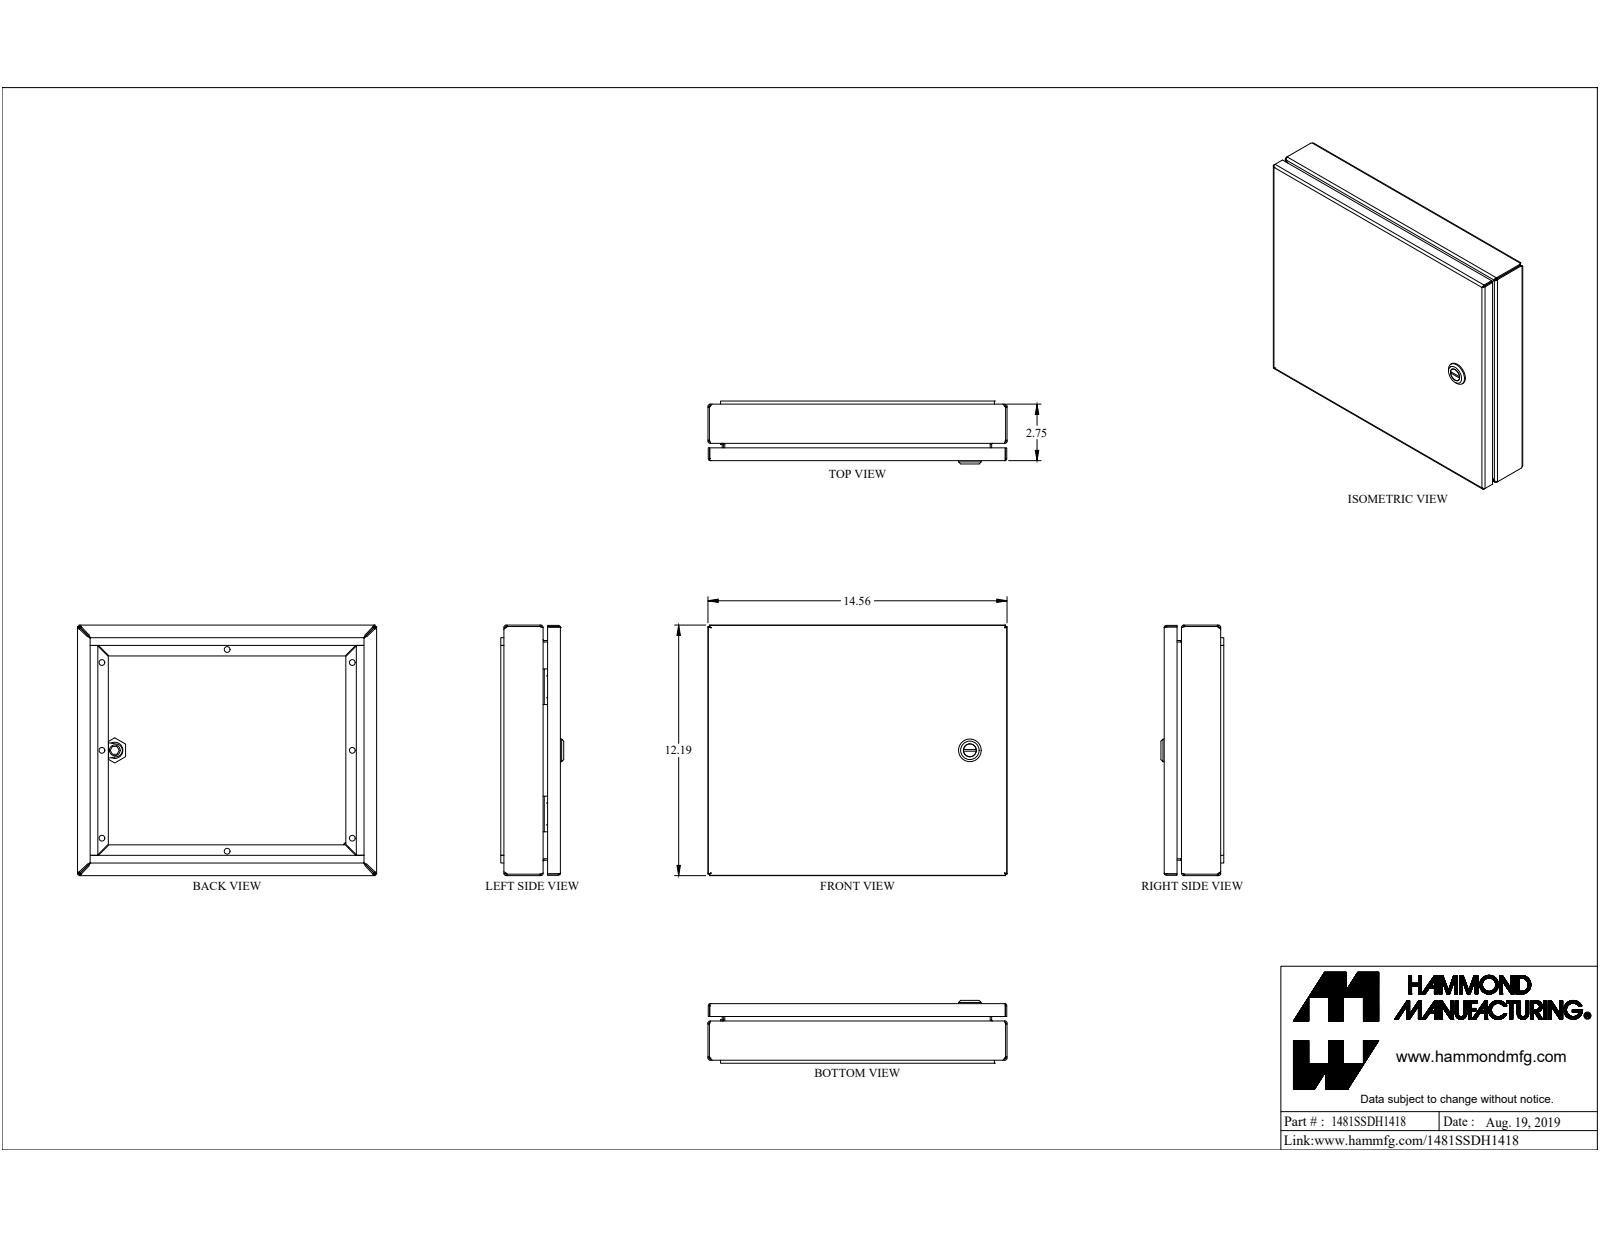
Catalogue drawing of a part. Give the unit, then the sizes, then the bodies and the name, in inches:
Units: inches
Overall size (bounding box): 14.56 × 12.19 × 3.06
Round holes (diameter × count): ⌀0.281 ×8, ⌀0.172 ×1, ⌀0.197 ×1, ⌀0.24 ×1, ⌀0.242 ×1, ⌀0.387 ×1, ⌀0.5 ×1, ⌀0.63 ×1, ⌀0.768 ×1
Round bosses / shafts (diameter × count): ⌀1.1 ×1, ⌀0.785 ×1, ⌀0.625 ×1, ⌀0.525 ×1, ⌀0.475 ×1, ⌀0.398 ×1, ⌀0.356 ×1, ⌀0.313 ×1
Partial cylindrical surfaces — rounded edges, fillets, slot ends (radius × count): R0.036 ×28, R0.108 ×28, R0.006 ×4, R0.062 ×4, R0.25 ×4, R0.499 ×4, R0.125 ×2, R0.021 ×1
Main face-to-face distances: 0.072, 2.578, 0.842, 1.736, 2.65, 12.118, 14.488, 2.506, 2.678, 1.836
Hole centre spacings: 6.125, 7.822, 11.017, 12.912, 12.184, 4.273, 4.273, 8.546
Volume: 41.9 in³ · Surface area: 1 090 in²
Bodies: 24 solids, 618 faces (374 planar, 147 cylindrical, 97 other)
Part name (STEP PRODUCT): 1481SSDH1418
STEP written by: SolidWorks 2019 (CONFIG_CONTROL_DESIGN)
